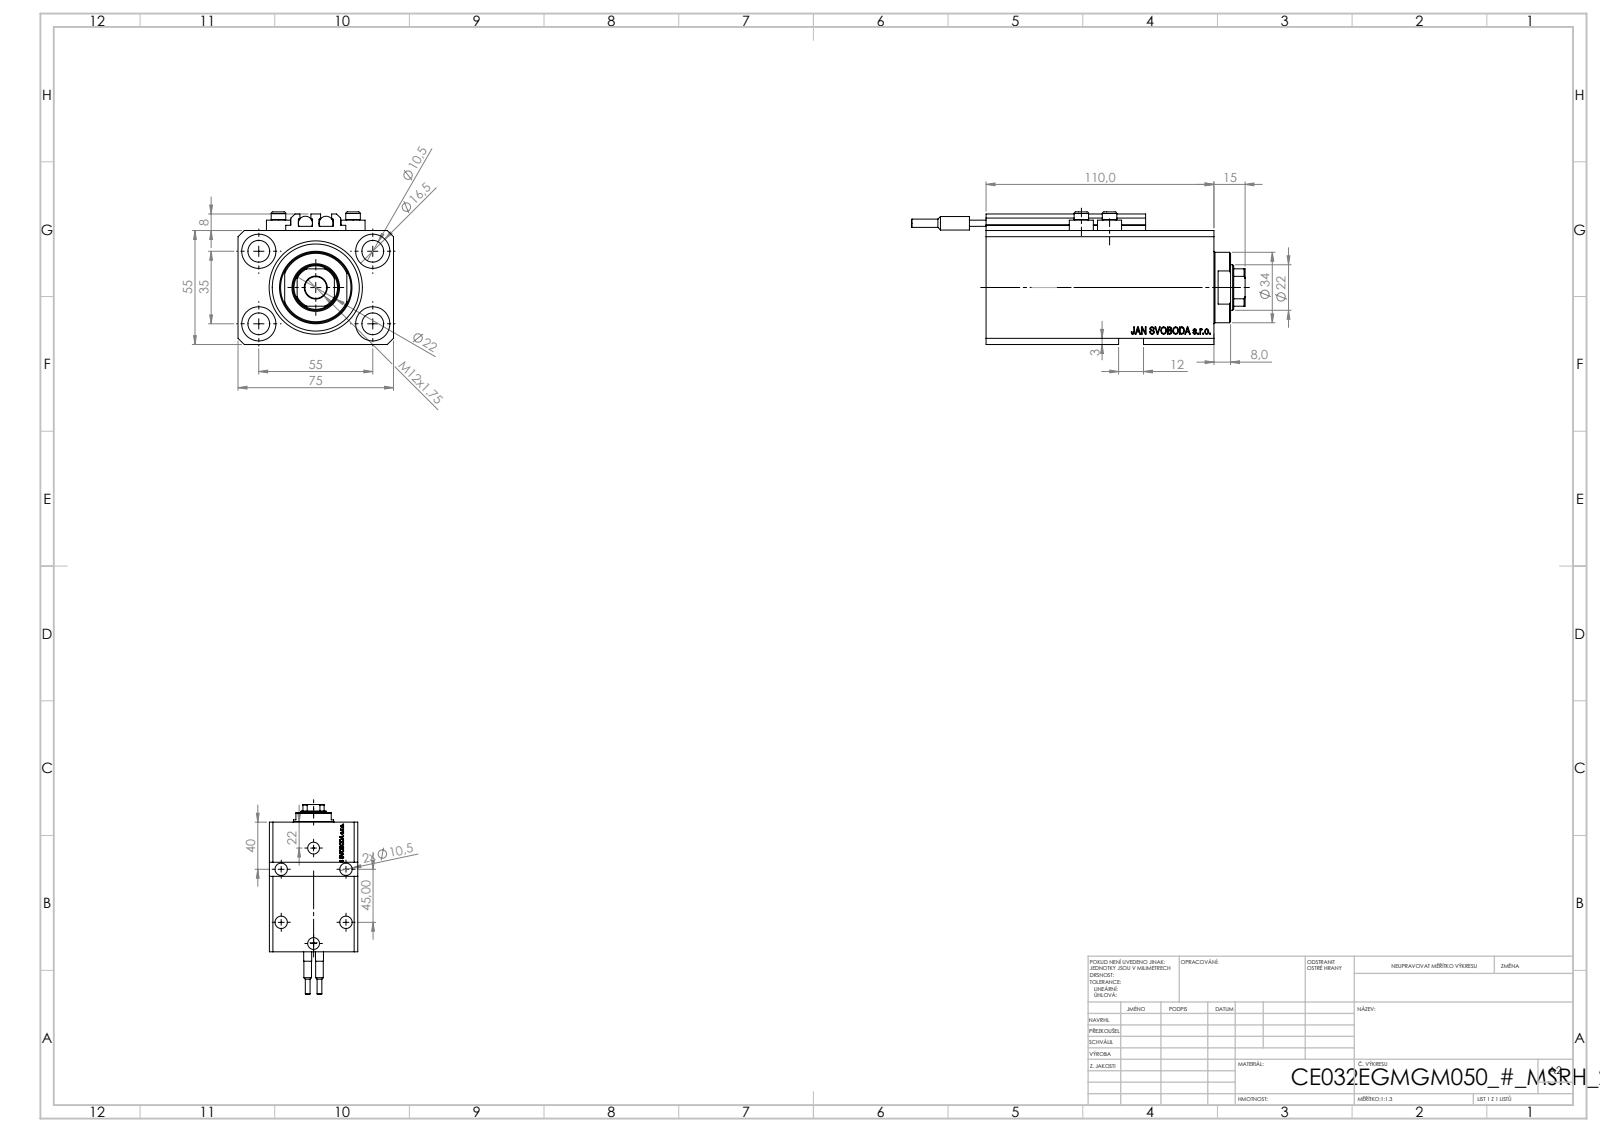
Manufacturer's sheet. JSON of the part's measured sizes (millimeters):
{"part_name": "SWITCH_V250CE; V250CE_E_Body; V250CE_C_VCP; ALLEN BOLT V250CE (+1 more)", "step_written_by": "SolidWorks 2019 (CONFIG_CONTROL_DESIGN)", "units": "millimeters", "bodies": {"solids": 10, "faces": 1136, "planar": 546, "cylindrical": 158, "other": 432}, "overall_size": [161, 75, 64], "volume_mm3": 384911, "surface_area_mm2": 98392, "round_holes": [[10.5, 9], [1.25, 4], [4, 4], [16.5, 4], [10, 2], [13.16, 2], [20, 2], [22, 1], [32, 1], [45, 1]], "round_bosses_or_shafts": [[11.6, 4], [7, 4], [6.8, 2], [6.5, 2], [4, 2], [34, 1]], "partial_cylinders_radius": [[0.2, 10], [10.5, 1]], "face_to_face_distances": [55, 75, 3, 15, 110, 57, 95, 9.9, 85.1, 100.1], "hole_center_spacings": [32.6, 32.87, 55, 68.74, 13.6, 14.09, 23.05, 25.81]}
